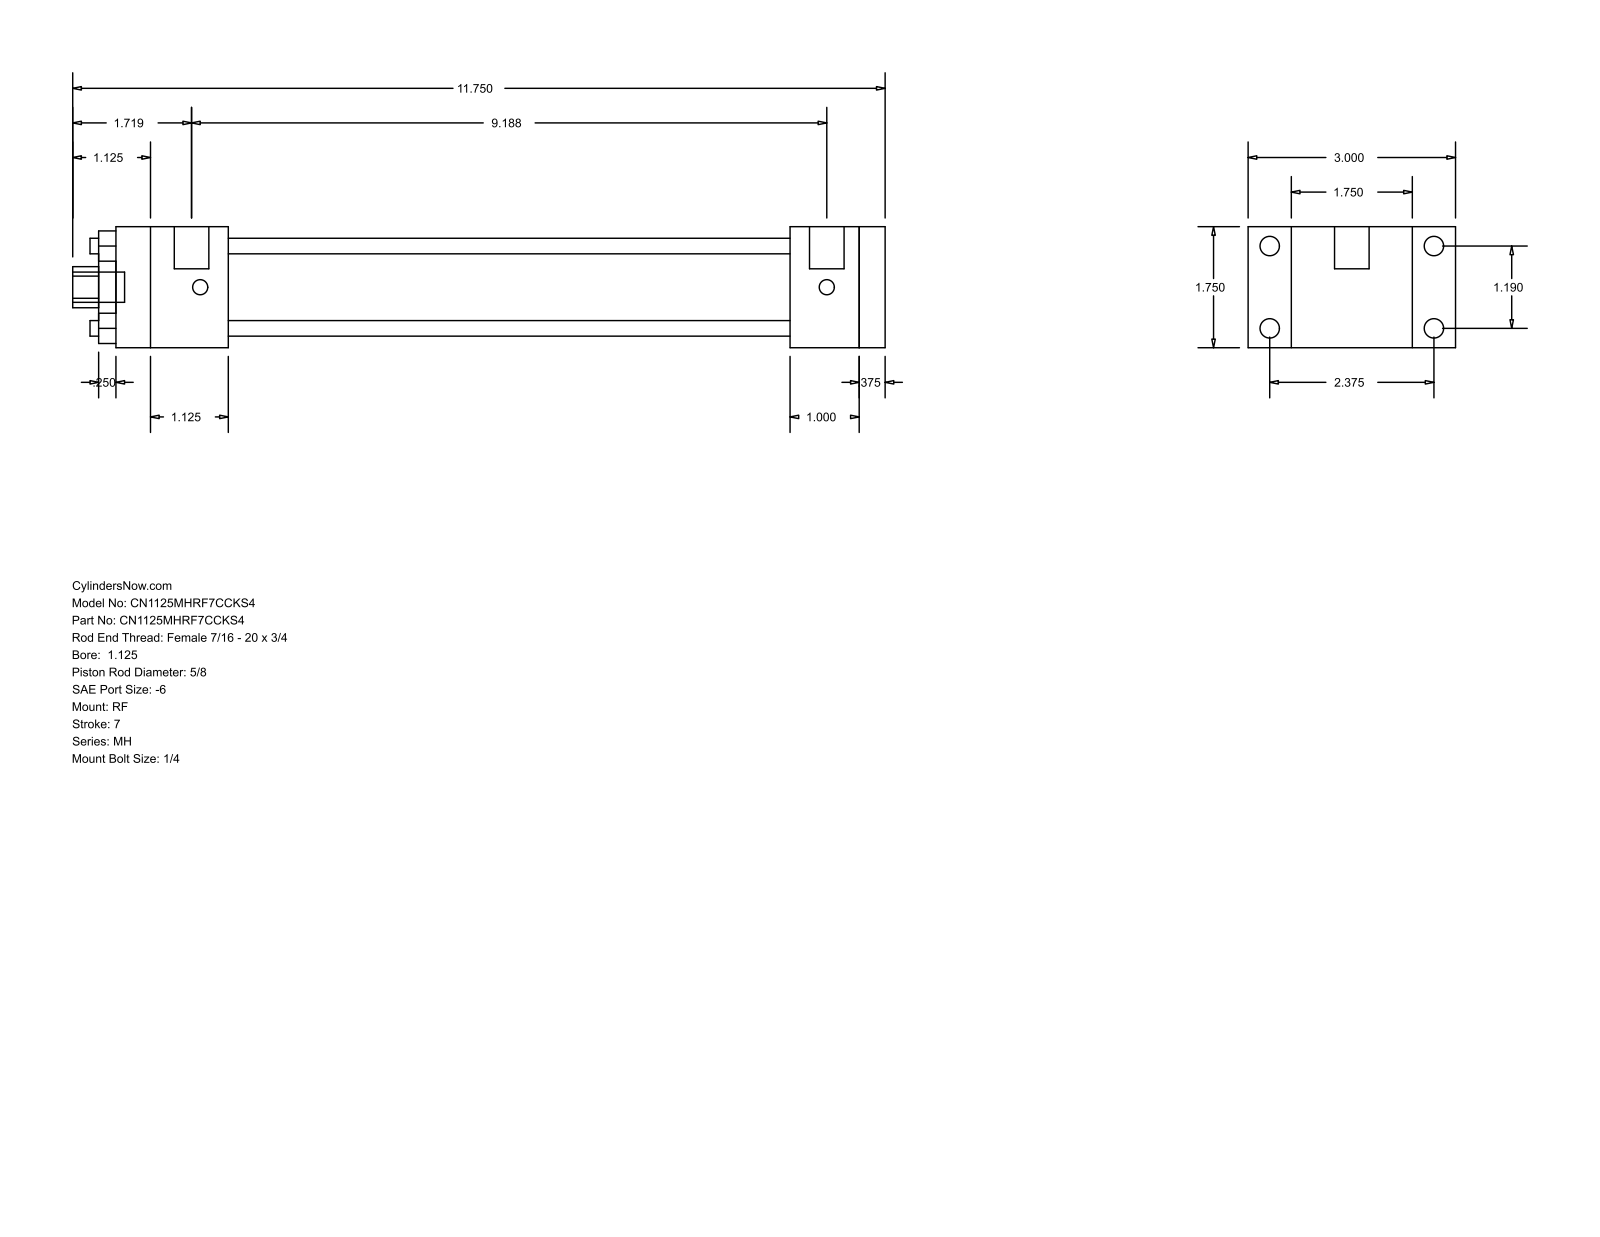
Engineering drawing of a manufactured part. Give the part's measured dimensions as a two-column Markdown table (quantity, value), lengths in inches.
| quantity | value |
| --- | --- |
| part name | MH_RF__0112_0.625 |
| STEP written by | GSSL Pune (CONFIG_CONTROL_DESIGN) |
| units | inches |
| bodies | 0 solids, 92 faces (64 planar, 28 cylindrical, 0 other) |
| overall size | 11.75 × 3 × 1.75 |
| round holes (diameter × count) | 0.225 × 4, 0.625 × 1, 1.125 × 1, 1.375 × 1 |
| round bosses / shafts (diameter × count) | 0.281 × 4, 0.219 × 4, 0.5 × 2, 0.437 × 1 |
| partial cylindrical surfaces (radius × count) | 0.297 × 1 |
| main face-to-face distances | 1.75, 0.375, 0.625, 9.125, 9.5, 8.125, 1, 1.375, 1.625, 9.75 |
| hole center spacings | 0.841, 1.19, 1.683 |
